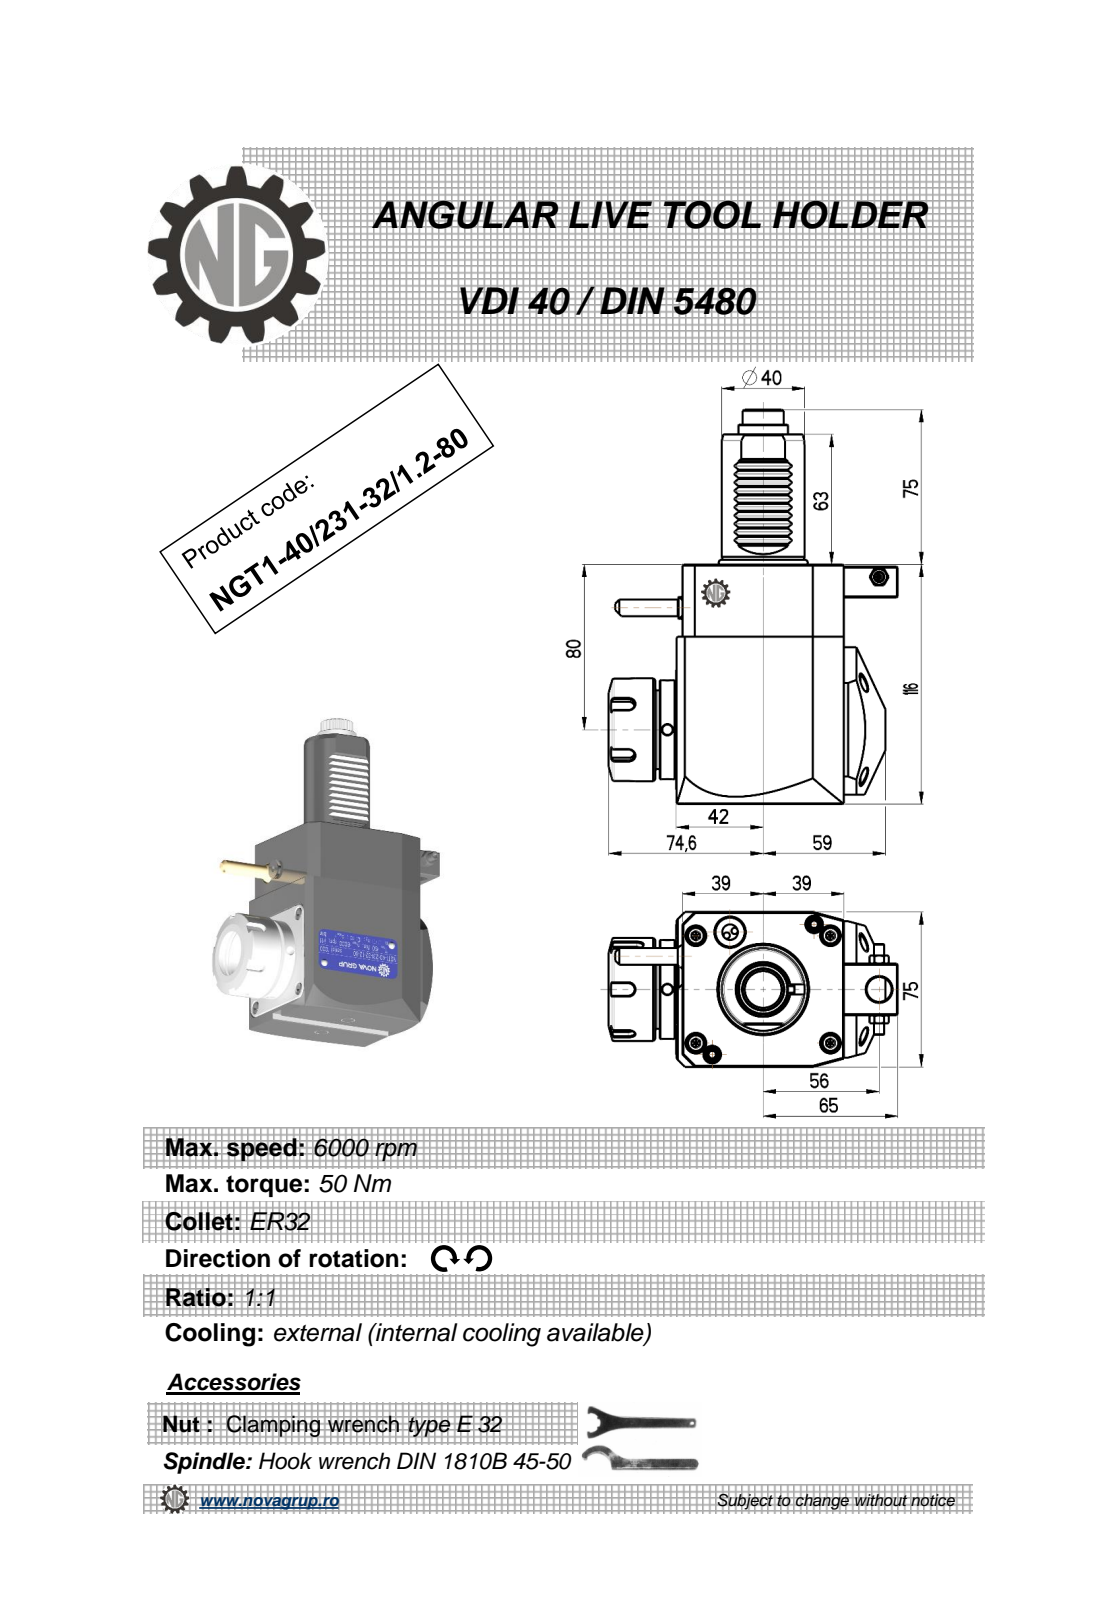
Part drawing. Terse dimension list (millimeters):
name: NGT1_40_231_32_1_2_80
written by: PRO/ENGINEER BY PARAMETRIC TECHNOLOGY CORPORATION, 2010280 (CONFIG_CONTROL_DESIGN)
unit: mm
bodies: 1 solid, 538 faces (199 planar, 185 cylindrical, 154 other)
size: 191 × 139.6 × 76.6
volume: 881 545 mm³; area: 70 474 mm²
holes: 3× ⌀5, 1× ⌀3, 1× ⌀4.2, 1× ⌀9.5, 1× ⌀12, 1× ⌀27
bosses: 1× ⌀50, 1× ⌀48, 1× ⌀41, 1× ⌀40, 1× ⌀24, 1× ⌀11.2, 1× ⌀8.96, 1× ⌀8
rounds: 48× R2.08, 12× R0.26, 10× R0.3, 6× R0.22, 5× R3, 1× R9.08, 1× R9.92, 1× R15
face distances: 75, 116, 81, 3, 78, 2.8, 80.8, 4.5, 7.5, 25
hole spacings: 20.3, 61.13, 71.5, 102.25, 126.22
